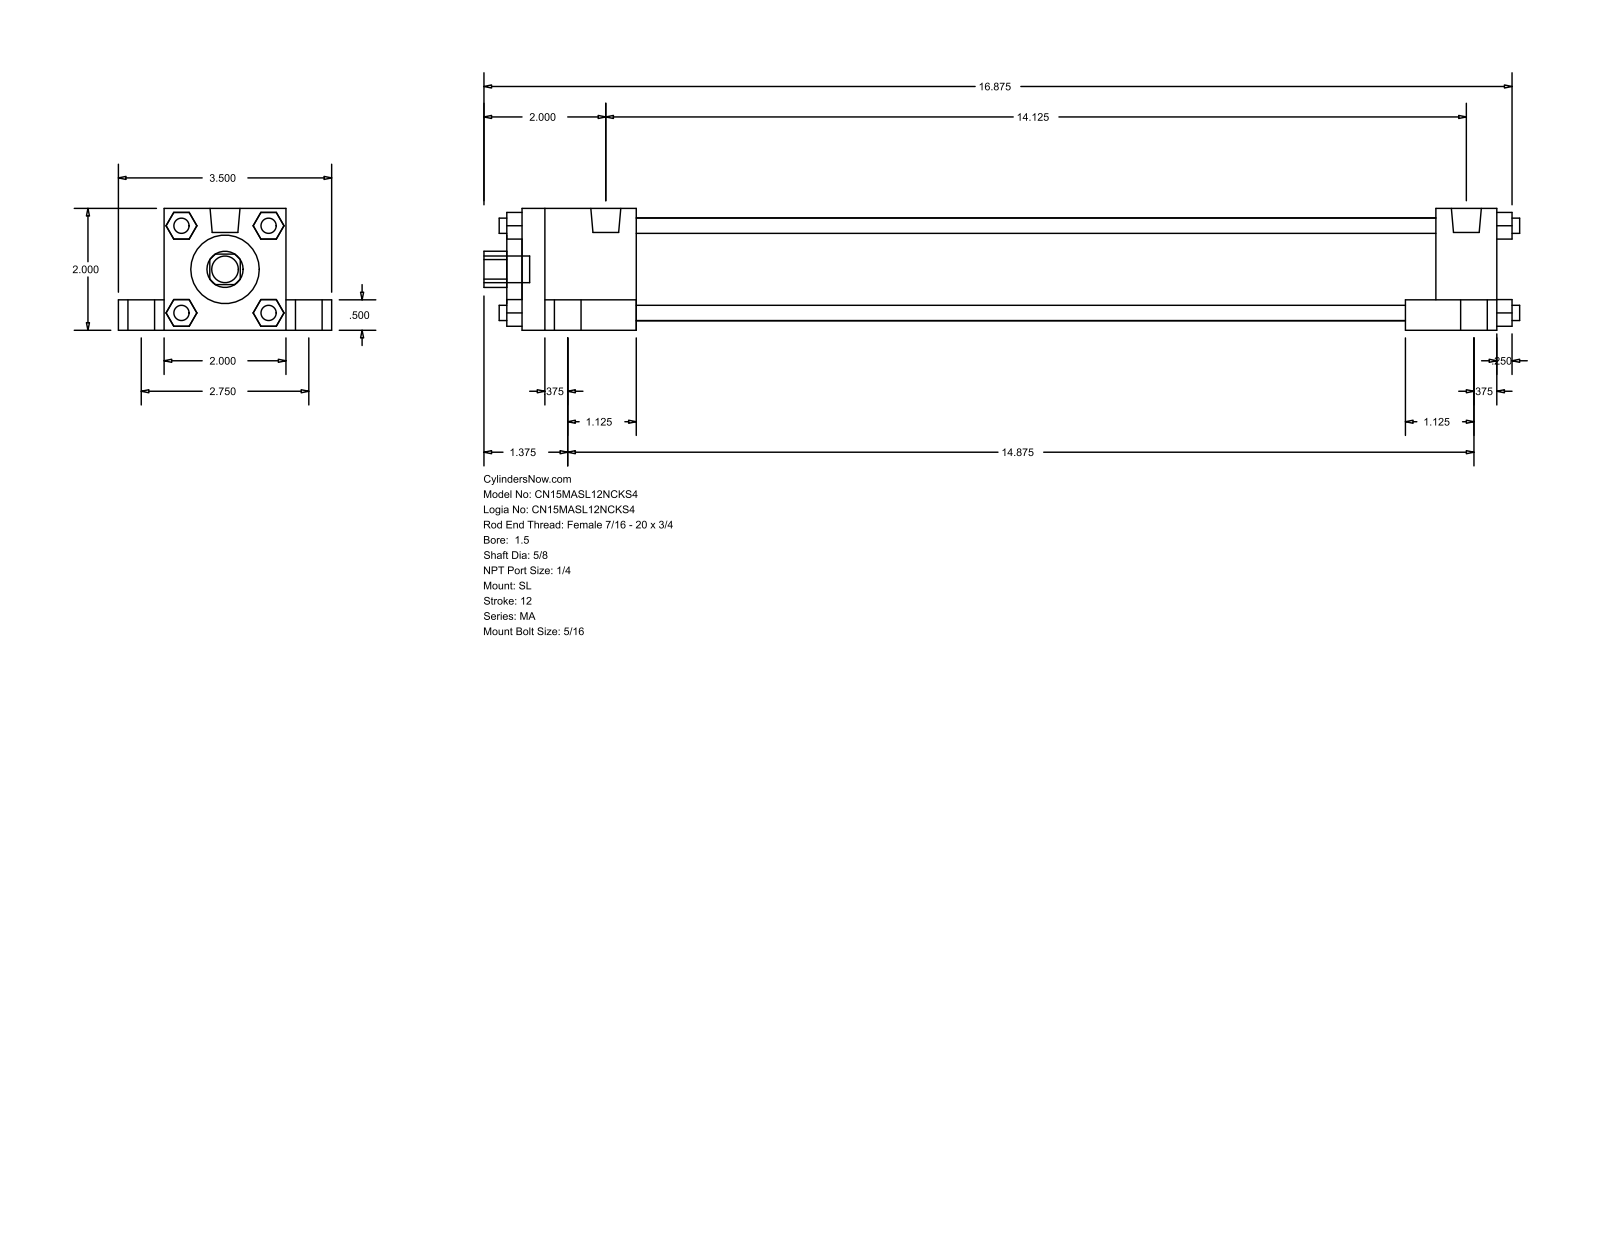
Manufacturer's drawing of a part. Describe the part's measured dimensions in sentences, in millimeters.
The part is named "MA_SL__0150_0.625". Its 3-D file was written by "GSSL Pune (CONFIG_CONTROL_DESIGN)". It is 0 solids with 148 faces: 112 planar, 36 cylindrical and 0 other. Overall it measures 431.8 by 88.9 by 50.8 millimeters. Round holes: 1 of diameter 15.88, 1 of diameter 28.57, 1 of diameter 42.93. Round bosses or shafts: 5 of diameter 11.11, 4 of diameter 17.46, 4 of diameter 7.94, 4 of diameter 6.35, 2 of diameter 12.49. Partial cylindrical surfaces (rounded edges, fillets, slot ends): 1 of radius 7.54. The main face-to-face distances are 50.8, 19.05, 38.1, 12.7, 69.85, 406.39, 6.35, 9.52, 412.74, 381.
